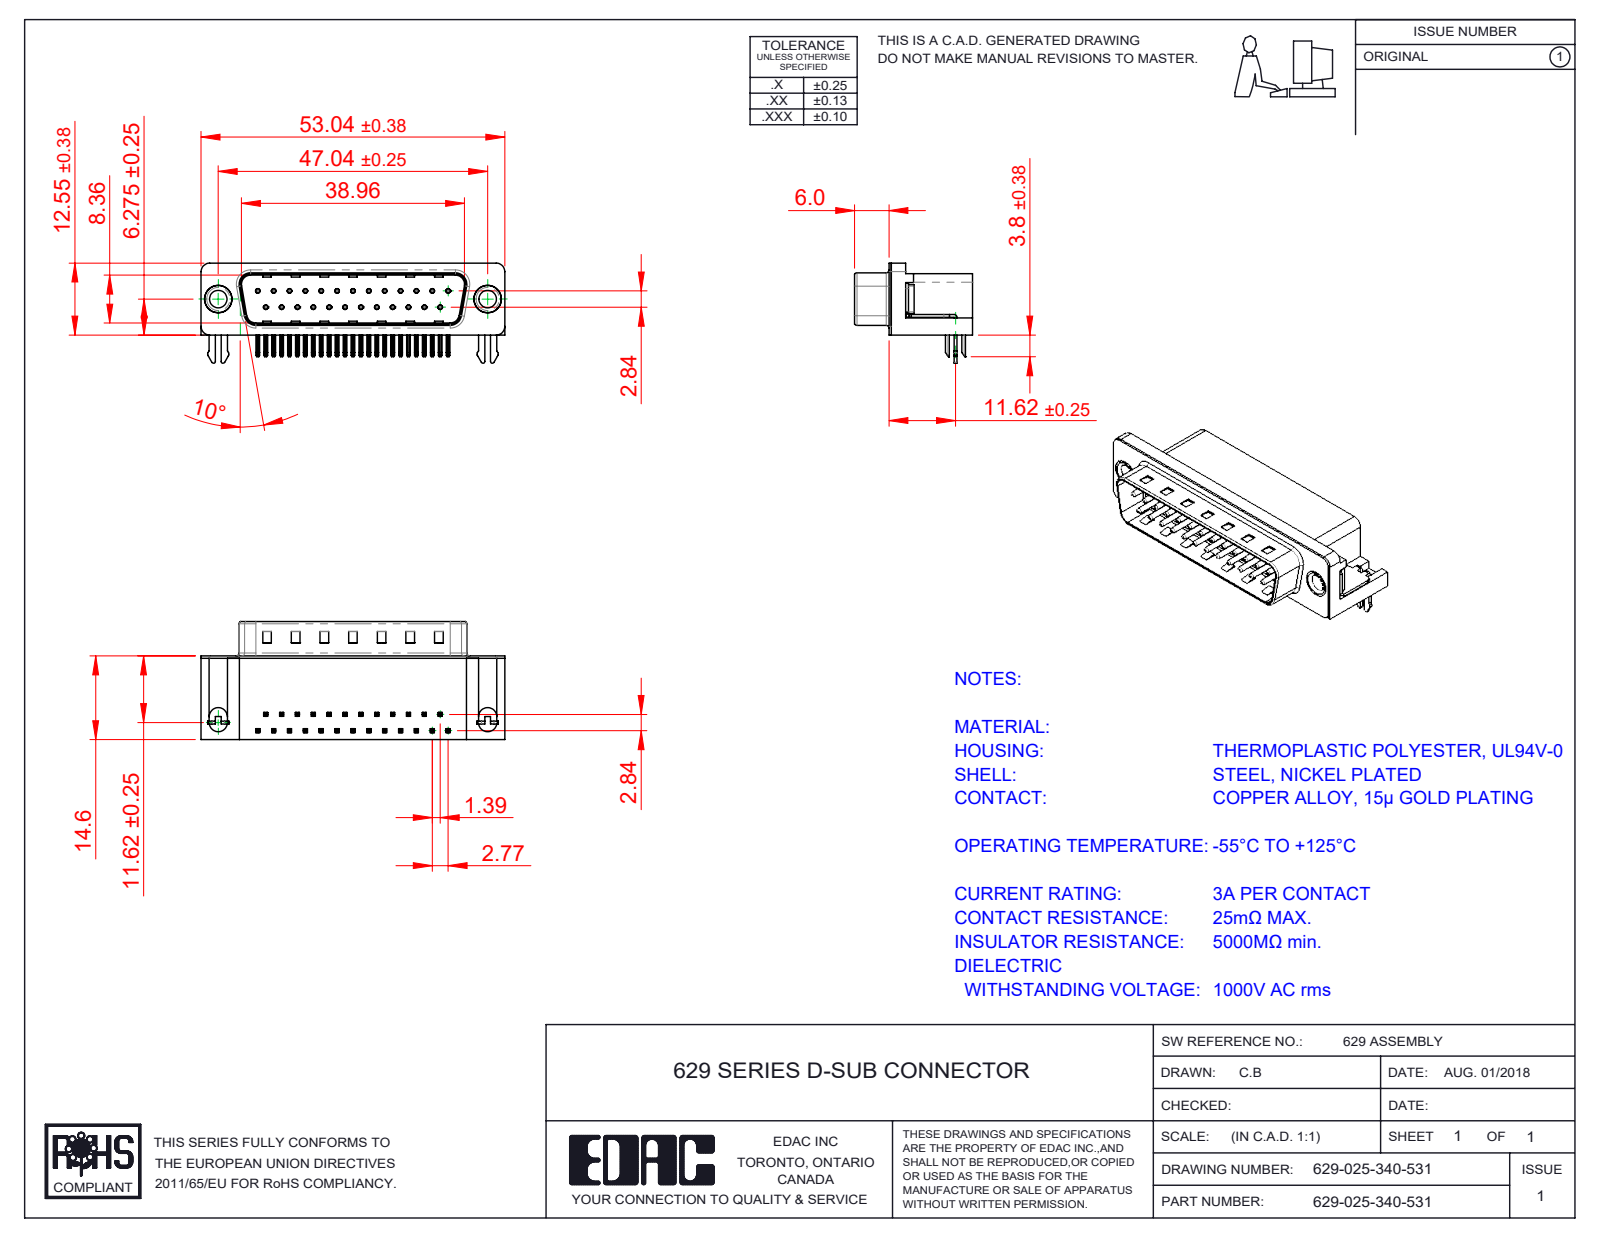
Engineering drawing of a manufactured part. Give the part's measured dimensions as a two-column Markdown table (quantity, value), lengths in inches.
| quantity | value |
| --- | --- |
| part name | 629 Housing_25 Socket; 629-025-340-531; 629 Shell_25 Socket; 629 Contact Bottom (+3 more) |
| STEP written by | SolidWorks 2020 (CONFIG_CONTROL_DESIGN) |
| units | inches |
| bodies | 31 solids, 2261 faces (1435 planar, 649 cylindrical, 177 other) |
| overall size | 2.088 × 0.811 × 0.688 |
| volume | 0.446 in³ |
| surface area | 12.75 in² |
| round holes (diameter × count) | 0.014 × 25, 0.031 × 25, 0.12 × 2, 0.157 × 2, 0.189 × 2, 0.197 × 2 |
| round bosses / shafts (diameter × count) | 0.03 × 25, 0.193 × 2, 0.187 × 2, 0.152 × 2 |
| partial cylindrical surfaces (radius × count) | 0.01 × 108, 0.005 × 50, 0.039 × 16, 0.02 × 14, 0.063 × 8, 0.059 × 7, 0.013 × 4, 0.035 × 4 |
| main face-to-face distances | 0.016, 0.408, 0.559, 0.083, 0.345, 0.067, 0.412, 0.428, 0.575, 0.461 |
| hole center spacings | 0.124, 0.109, 0.218, 0.327, 0.436, 0.545, 0.654, 0.198 |
